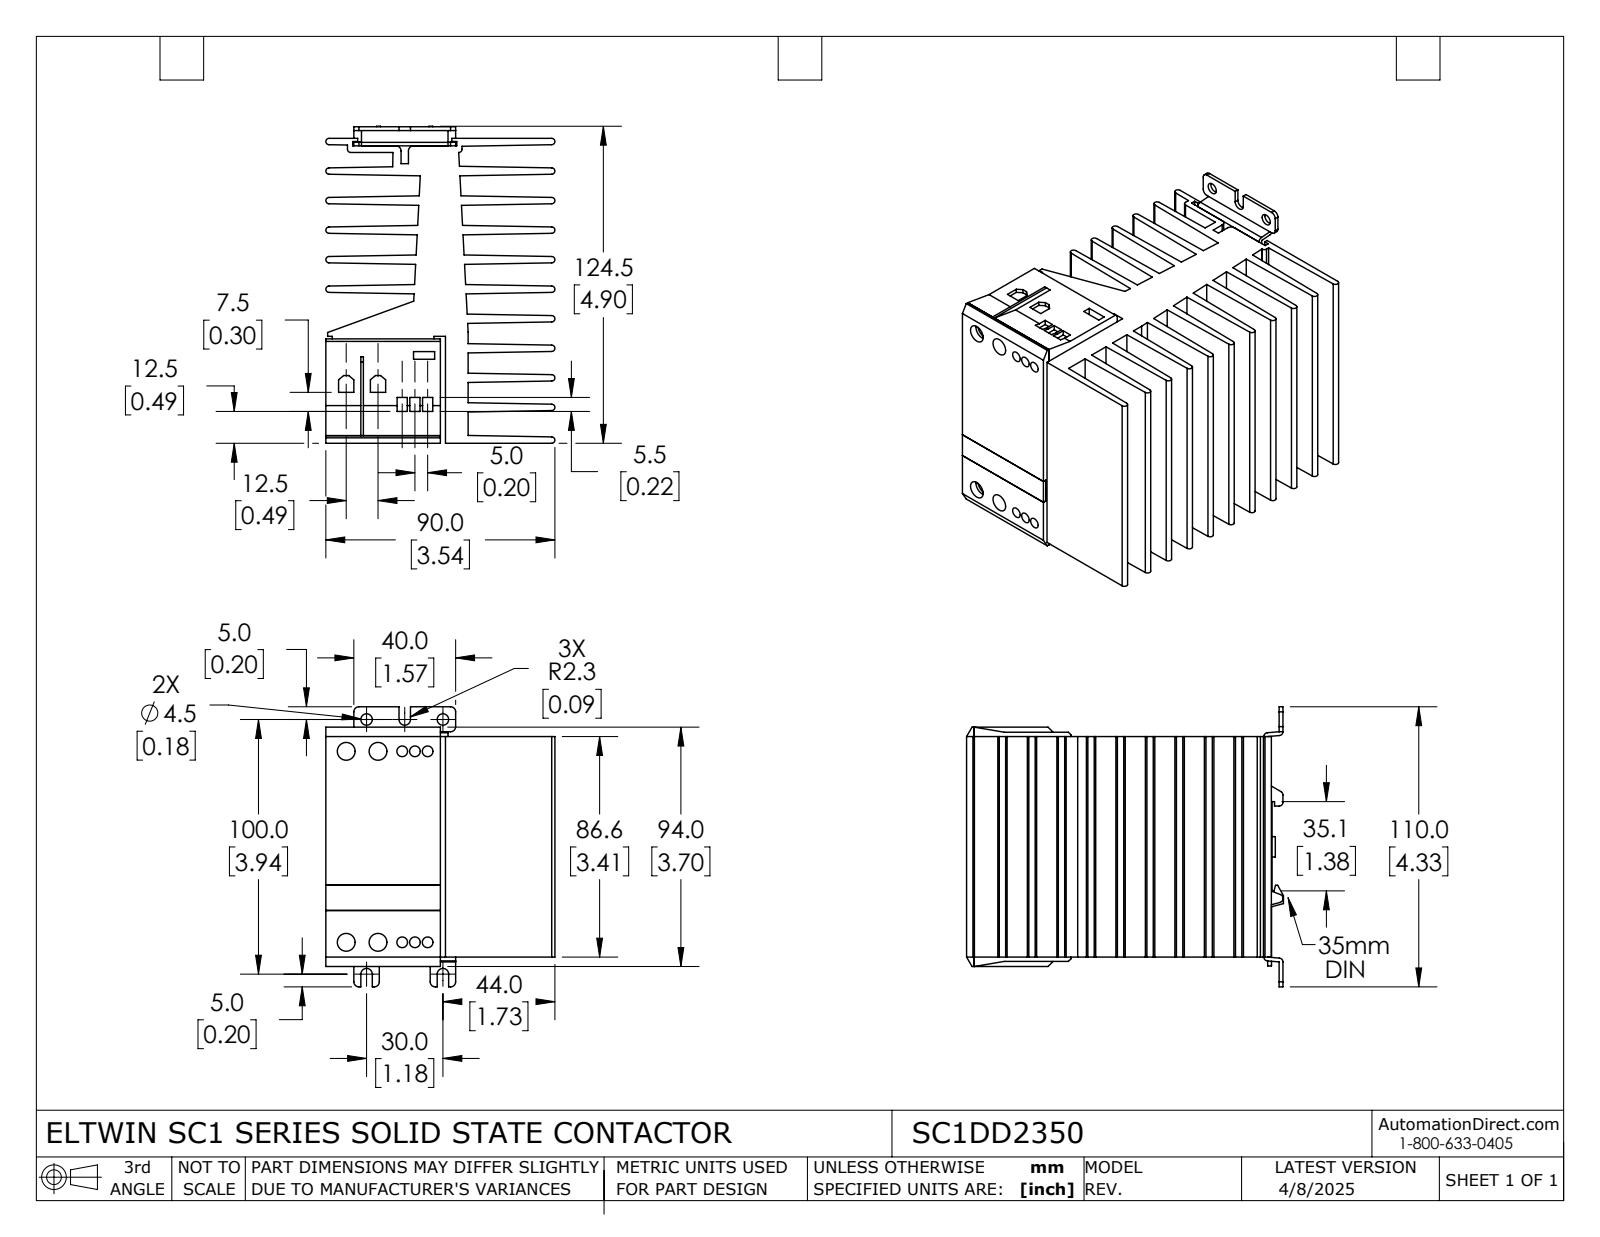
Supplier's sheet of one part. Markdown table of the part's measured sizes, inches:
| quantity | value |
| --- | --- |
| part name | SC1DD2350 |
| STEP written by | SolidWorks 2021 (AUTOMOTIVE_DESIGN) |
| units | inches |
| bodies | 7 solids, 404 faces (294 planar, 110 cylindrical, 0 other) |
| overall size | 4.902 × 4.331 × 3.543 |
| volume | 31.2 in³ |
| surface area | 277.4 in² |
| round holes (diameter × count) | 0.165 × 6, 0.173 × 6, 0.276 × 4, 0.177 × 2, 0.315 × 2 |
| round bosses / shafts (diameter × count) | 0.315 × 3 |
| partial cylindrical surfaces (radius × count) | 0.049 × 19, 0.079 × 18, 0.059 × 10, 0.051 × 4, 0.089 × 3 |
| main face-to-face distances | 0.457, 0.913, 1.37, 0.159, 0.3, 0.157, 1.827, 1.669, 1.828, 2.126 |
| hole center spacings | 2.953, 0.197, 2.959, 0.374, 0.394, 0.492, 0.571, 0.768 |
